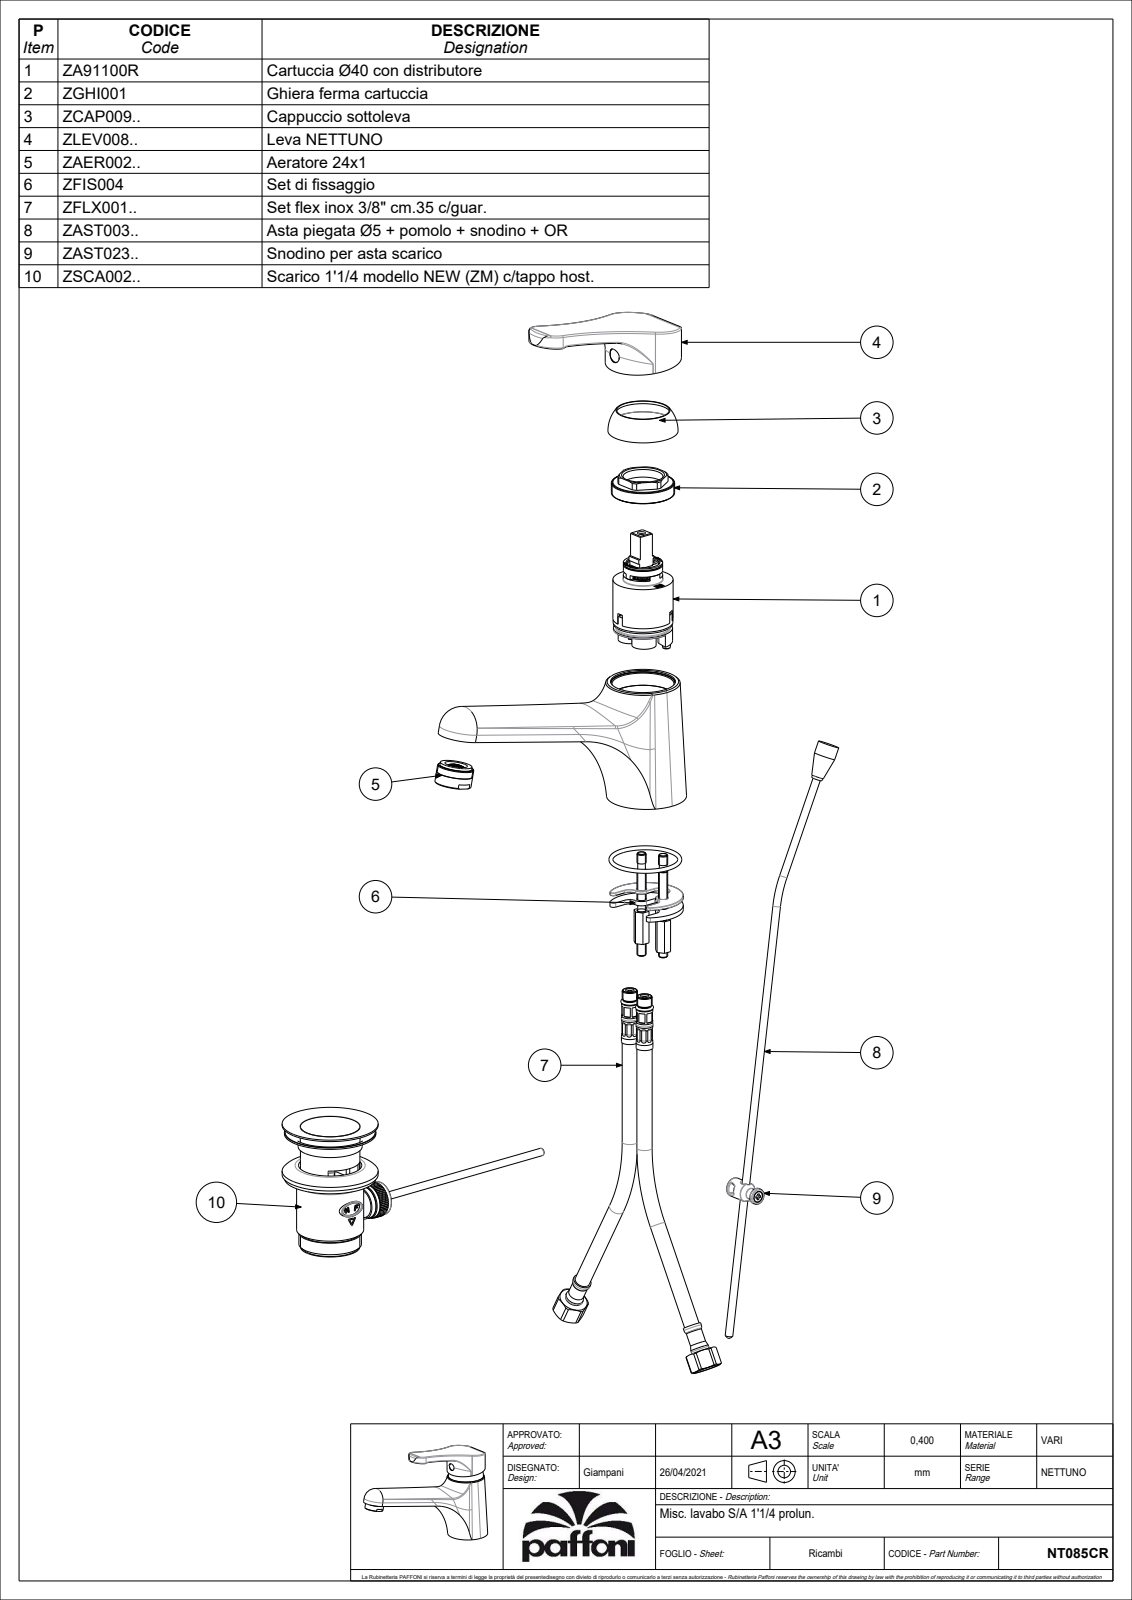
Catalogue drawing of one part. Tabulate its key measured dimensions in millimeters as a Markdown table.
| quantity | value |
| --- | --- |
| part name | NT085CR |
| STEP written by | CREO PARAMETRIC BY PTC INC, 2020044 (CONFIG_CONTROL_DESIGN) |
| units | millimeters |
| bodies | 1 solid, 283 faces (53 planar, 85 cylindrical, 145 other) |
| overall size | 217.98 × 116.74 × 52.5 |
| volume | 188 577 mm³ |
| surface area | 73 615 mm² |
| round holes (diameter × count) | 5 × 2, 5.5 × 2, 7 × 2, 9 × 2, 11 × 2, 9.4 × 1, 16 × 1, 20 × 1, 21 × 1, 23 × 1, 24.5 × 1, 39.1 × 1 |
| round bosses / shafts (diameter × count) | 10 × 2, 50 × 1, 42 × 1, 24 × 1, 14 × 1, 5 × 1 |
| partial cylindrical surfaces (radius × count) | 2.5 × 6, 2 × 4, 5 × 2, 7.5 × 2, 135 × 2, 1 × 1, 10 × 1, 13 × 1 |
| main face-to-face distances | 17.5, 21.5, 3, 4, 67.96, 33, 7.95, 46.46, 6.5, 50.46 |
| hole center spacings | 1.03, 1.83, 8.17, 8.6, 10.97, 12.01, 12.08, 13.09 |
